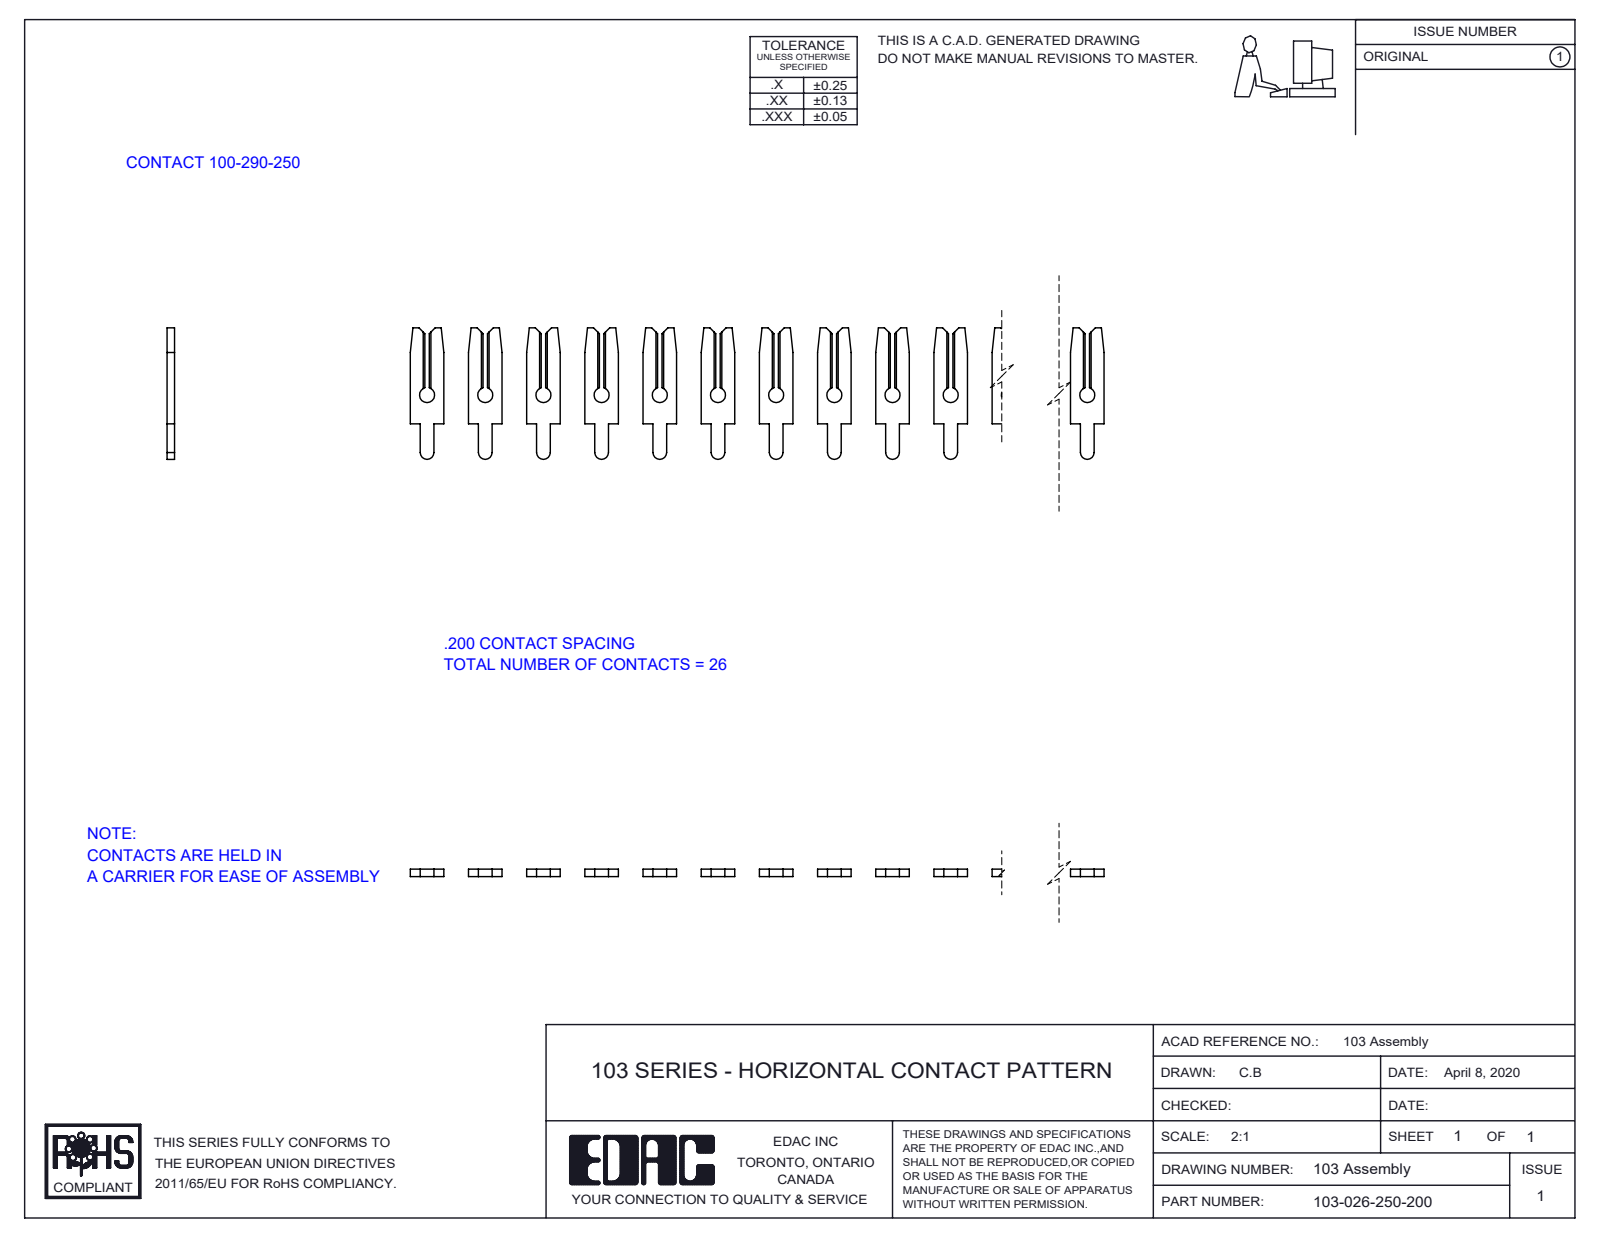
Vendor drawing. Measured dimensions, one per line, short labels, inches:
name: 103-026-250-200; 100-290-001_100-290-250
written by: SolidWorks 2016 (CONFIG_CONTROL_DESIGN)
unit: in
bodies: 26 solids, 624 faces (520 planar, 104 cylindrical, 0 other)
size: 5.115 × 0.452 × 0.026
volume: 0.025 in³; area: 2.956 in²
holes: 26× ⌀0.052
rounds: 26× R0.024
face distances: 0.026, 0.141, 0.2, 0.4, 0.283, 0.848, 0.6, 0.99, 0.707, 0.8
hole spacings: 0.2, 0.4, 0.6, 0.8, 1, 1.2, 1.4, 1.6
